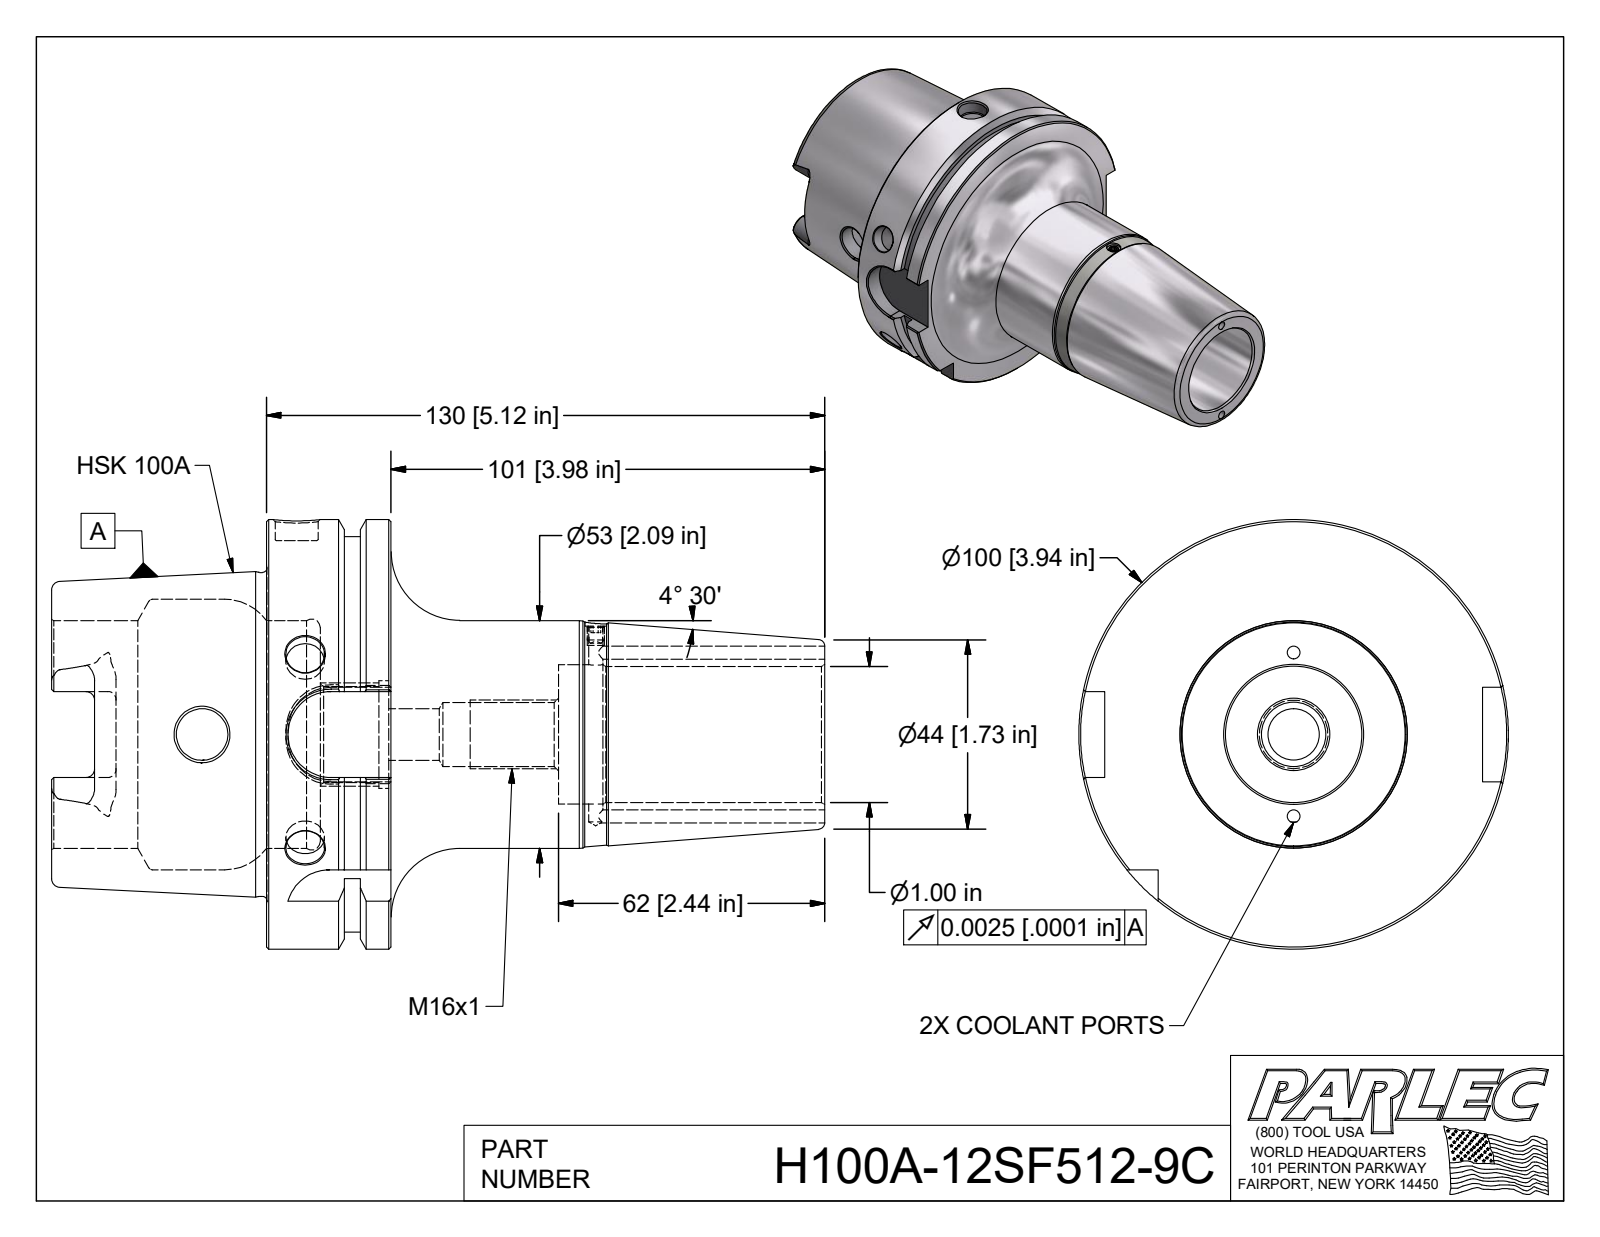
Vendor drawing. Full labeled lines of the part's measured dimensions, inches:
STEP written by: Autodesk Inventor 2018 (AUTOMOTIVE_DESIGN)
Units: inches
Bodies: 1 solid, 153 faces (49 planar, 42 cylindrical, 62 other)
Overall size (bounding box): 7.087 × 3.937 × 3.937
Volume: 25.04 in³ · Surface area: 113.3 in²
Round holes (diameter × count): ⌀0.118 ×2, ⌀0.354 ×2, ⌀0.472 ×2, ⌀0.128 ×1, ⌀0.197 ×1, ⌀0.394 ×1, ⌀0.587 ×1, ⌀0.881 ×1, ⌀0.985 ×1, ⌀1.248 ×1, ⌀1.278 ×1, ⌀2.087 ×1
Round bosses / shafts (diameter × count): ⌀3.937 ×1, ⌀3.622 ×1, ⌀2.967 ×1
Partial cylindrical surfaces — rounded edges, fillets, slot ends (radius × count): R0.079 ×6, R0.192 ×4, R0.394 ×4
Main face-to-face distances: 1.142, 0.492, 0.65, 1.969, 2.461, 3.11, 4.646, 2.677, 2.185, 1.535
Hole centre spacings: 0.75, 1.5, 2.743
